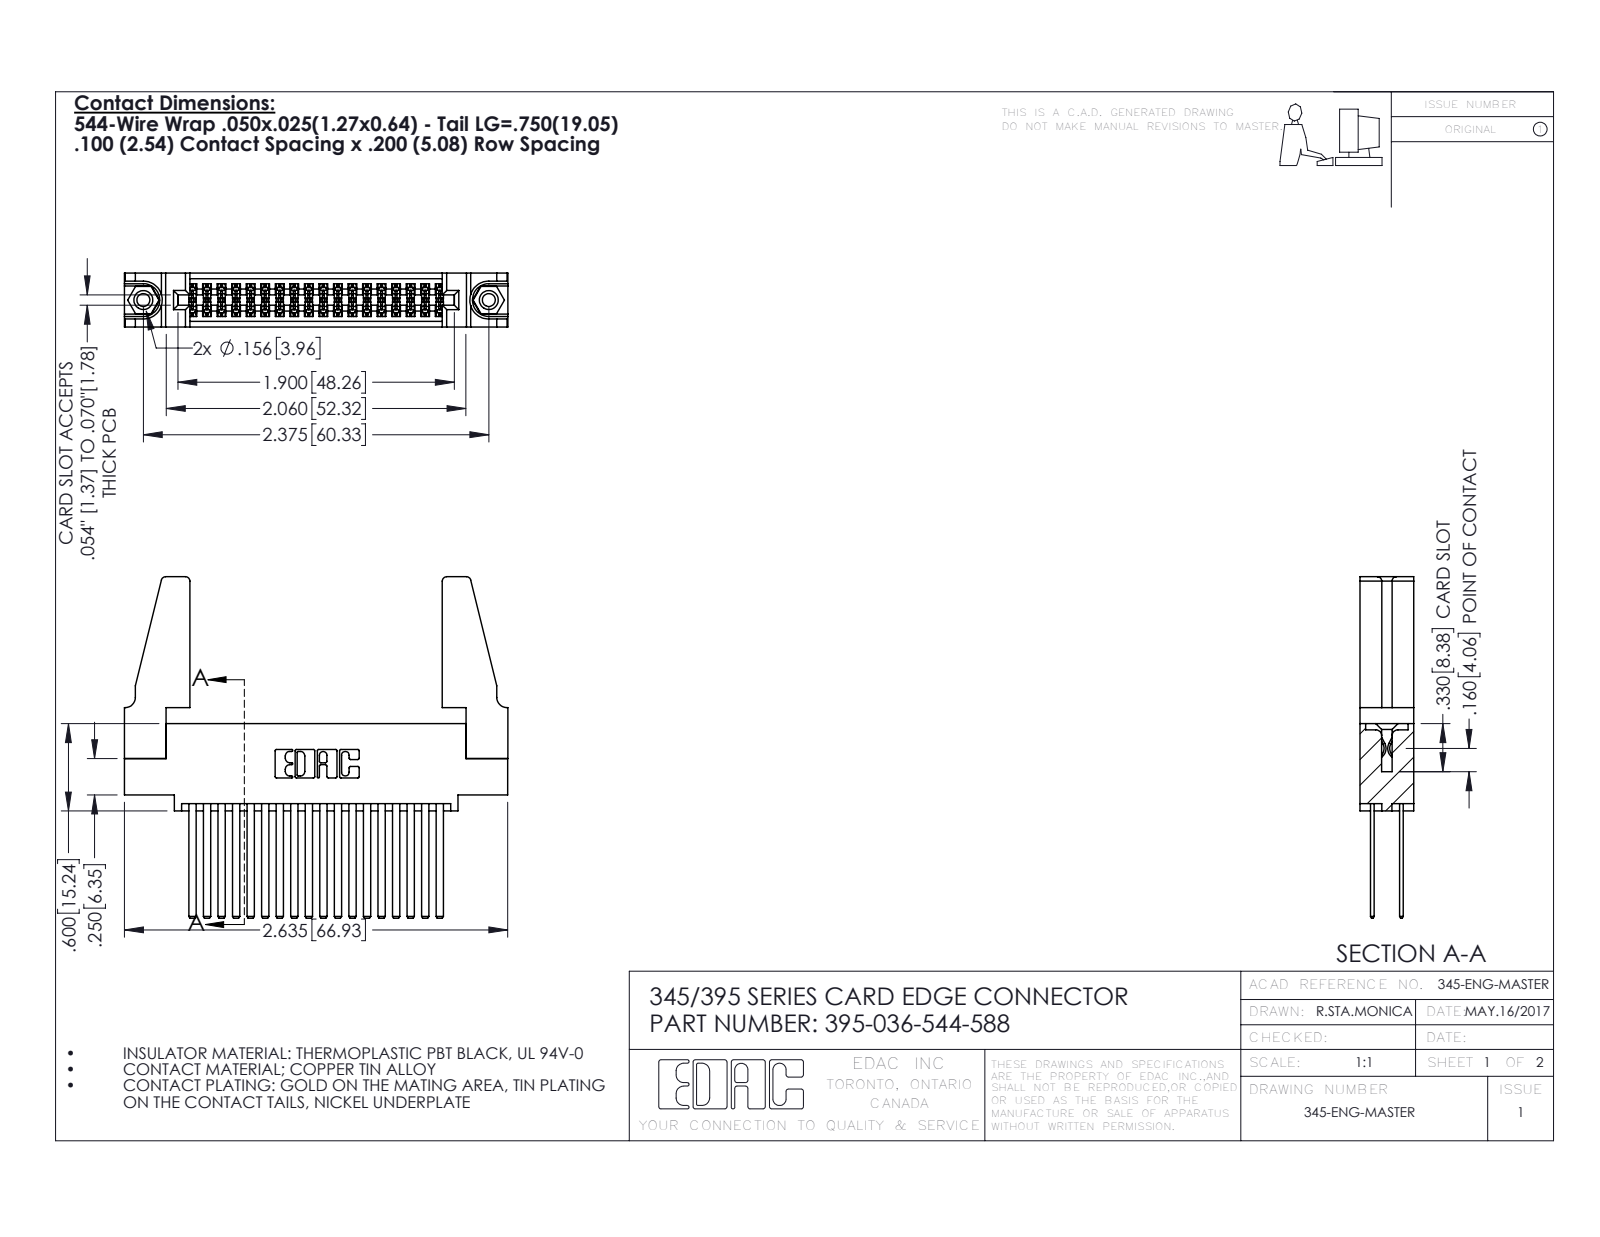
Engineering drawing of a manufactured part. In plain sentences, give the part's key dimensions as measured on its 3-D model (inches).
The part is named "345-220-078_345-220-088; 395-036-544-588; 345-292-001_345-293-144; 345 Part_0.110 Offset - 0.156 Dia-TH (+1 more)". Its 3-D file was written by "SolidWorks 2016 (CONFIG_CONTROL_DESIGN)". It is 41 solids with 1838 faces: 1200 planar, 622 cylindrical and 16 other. Overall it measures 2.636 by 2.347 by 0.37 inches. Its volume is 0.608 cubic inches and its surface area 21.93 square inches. Round holes: 2 of diameter 0.089, 2 of diameter 0.125, 2 of diameter 0.156, 1 of diameter 0.064. Round bosses or shafts: 2 of diameter 0.155. Partial cylindrical surfaces (rounded edges, fillets, slot ends): 54 of radius 0.006, 22 of radius 0.01, 8 of radius 0.03, 6 of radius 0.007, 6 of radius 0.031, 3 of radius 0.026, 2 of radius 0.014, 2 of radius 0.019. The main face-to-face distances are 0.072, 0.298, 0.2, 0.098, 0.272, 0.025, 0.37, 0.225, 0.175, 0.05. The hole center spacings are 0.27, 2.141, 2.375.
